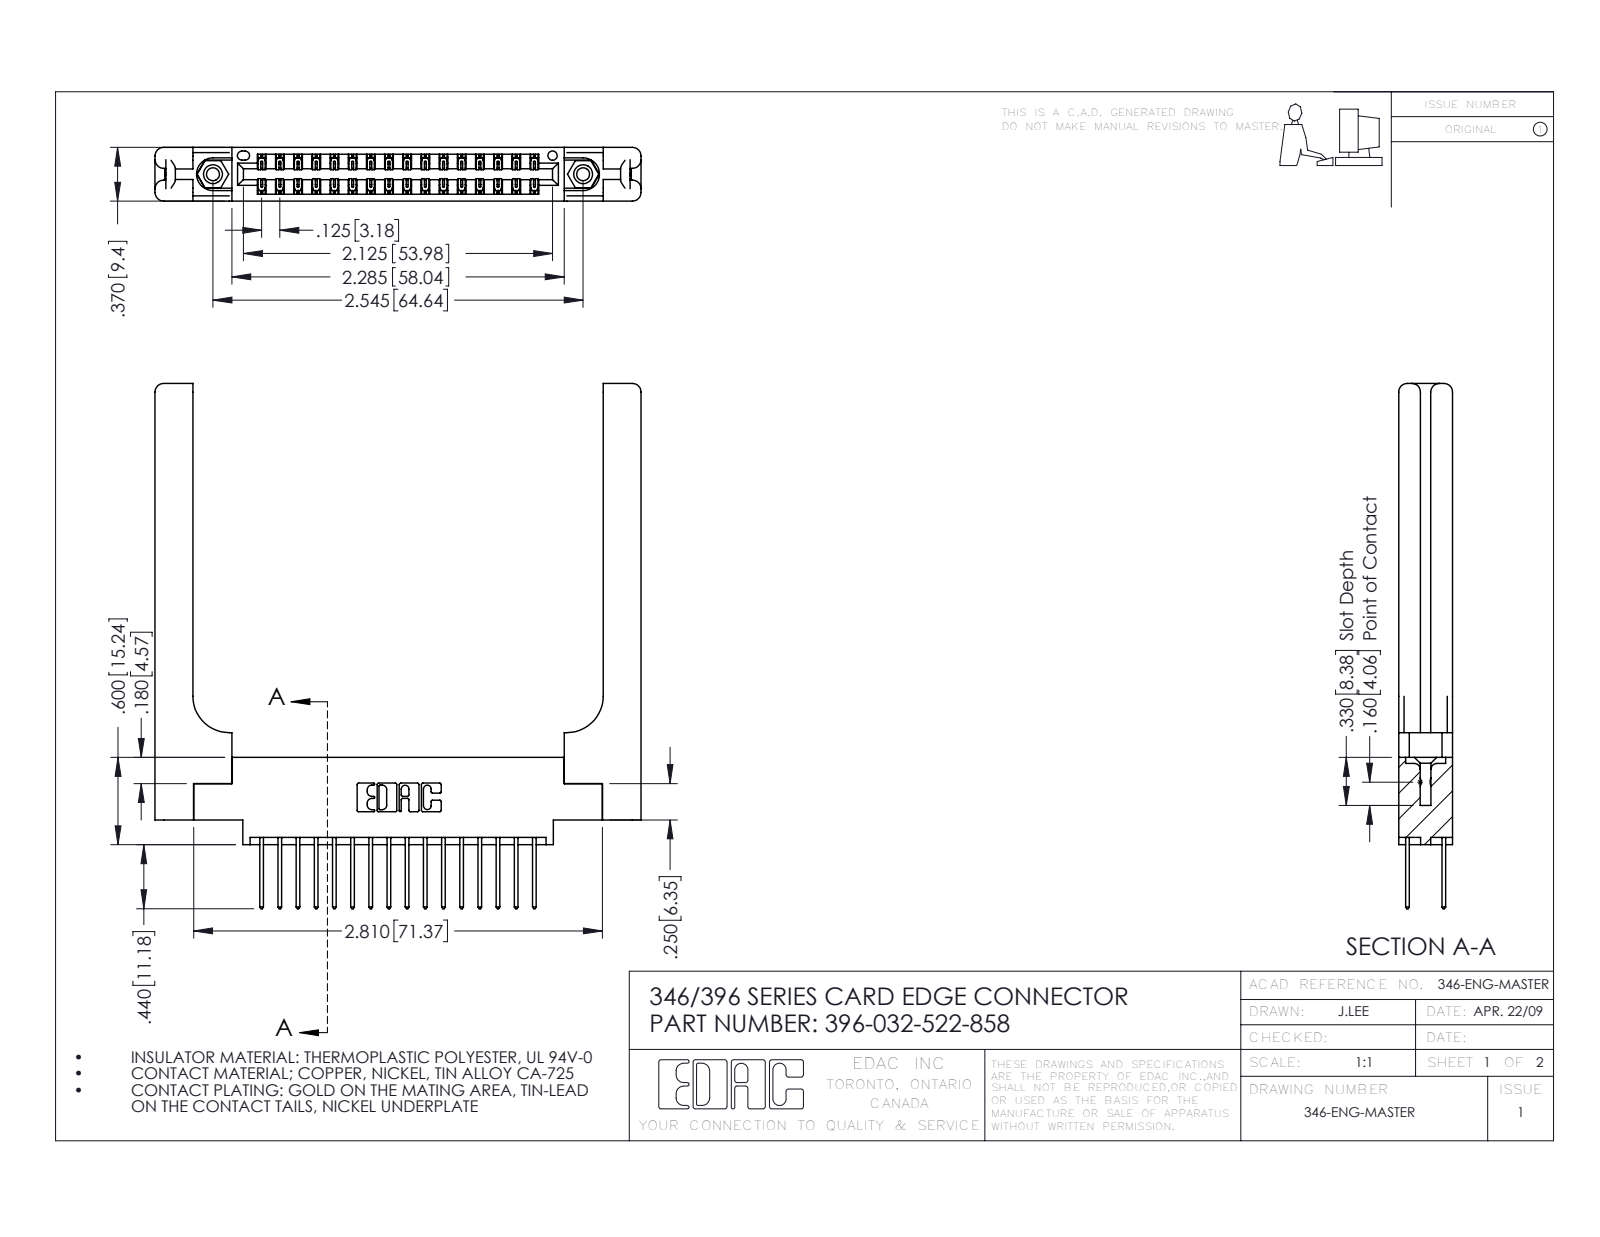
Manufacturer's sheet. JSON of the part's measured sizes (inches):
{"part_name": "346-220-058_345-220-058; 345-250-001_345-250-001-102; 396-032-522-858; 345-292-001_345-293-122 (+1 more)", "step_written_by": "SolidWorks 2016 (CONFIG_CONTROL_DESIGN)", "units": "inches", "bodies": {"solids": 37, "faces": 2046, "planar": 1348, "cylindrical": 638, "other": 60}, "overall_size": [3.61, 3.341, 0.37], "volume_in3": 0.946, "surface_area_in2": 24.99, "round_holes": [[0.089, 2], [0.125, 2], [0.156, 2], [0.064, 1]], "round_bosses_or_shafts": [[0.155, 2]], "partial_cylinders_radius": [[0.006, 48], [0.01, 32], [0.01, 22], [0.06, 16], [0.007, 6], [0.031, 6], [0.026, 3], [0.014, 2]], "face_to_face_distances": [0.37, 0.072, 0.048, 0.322, 0.148, 0.15, 0.25, 0.025, 0.298, 0.077], "hole_center_spacings": [0.246, 2.338, 2.545]}
